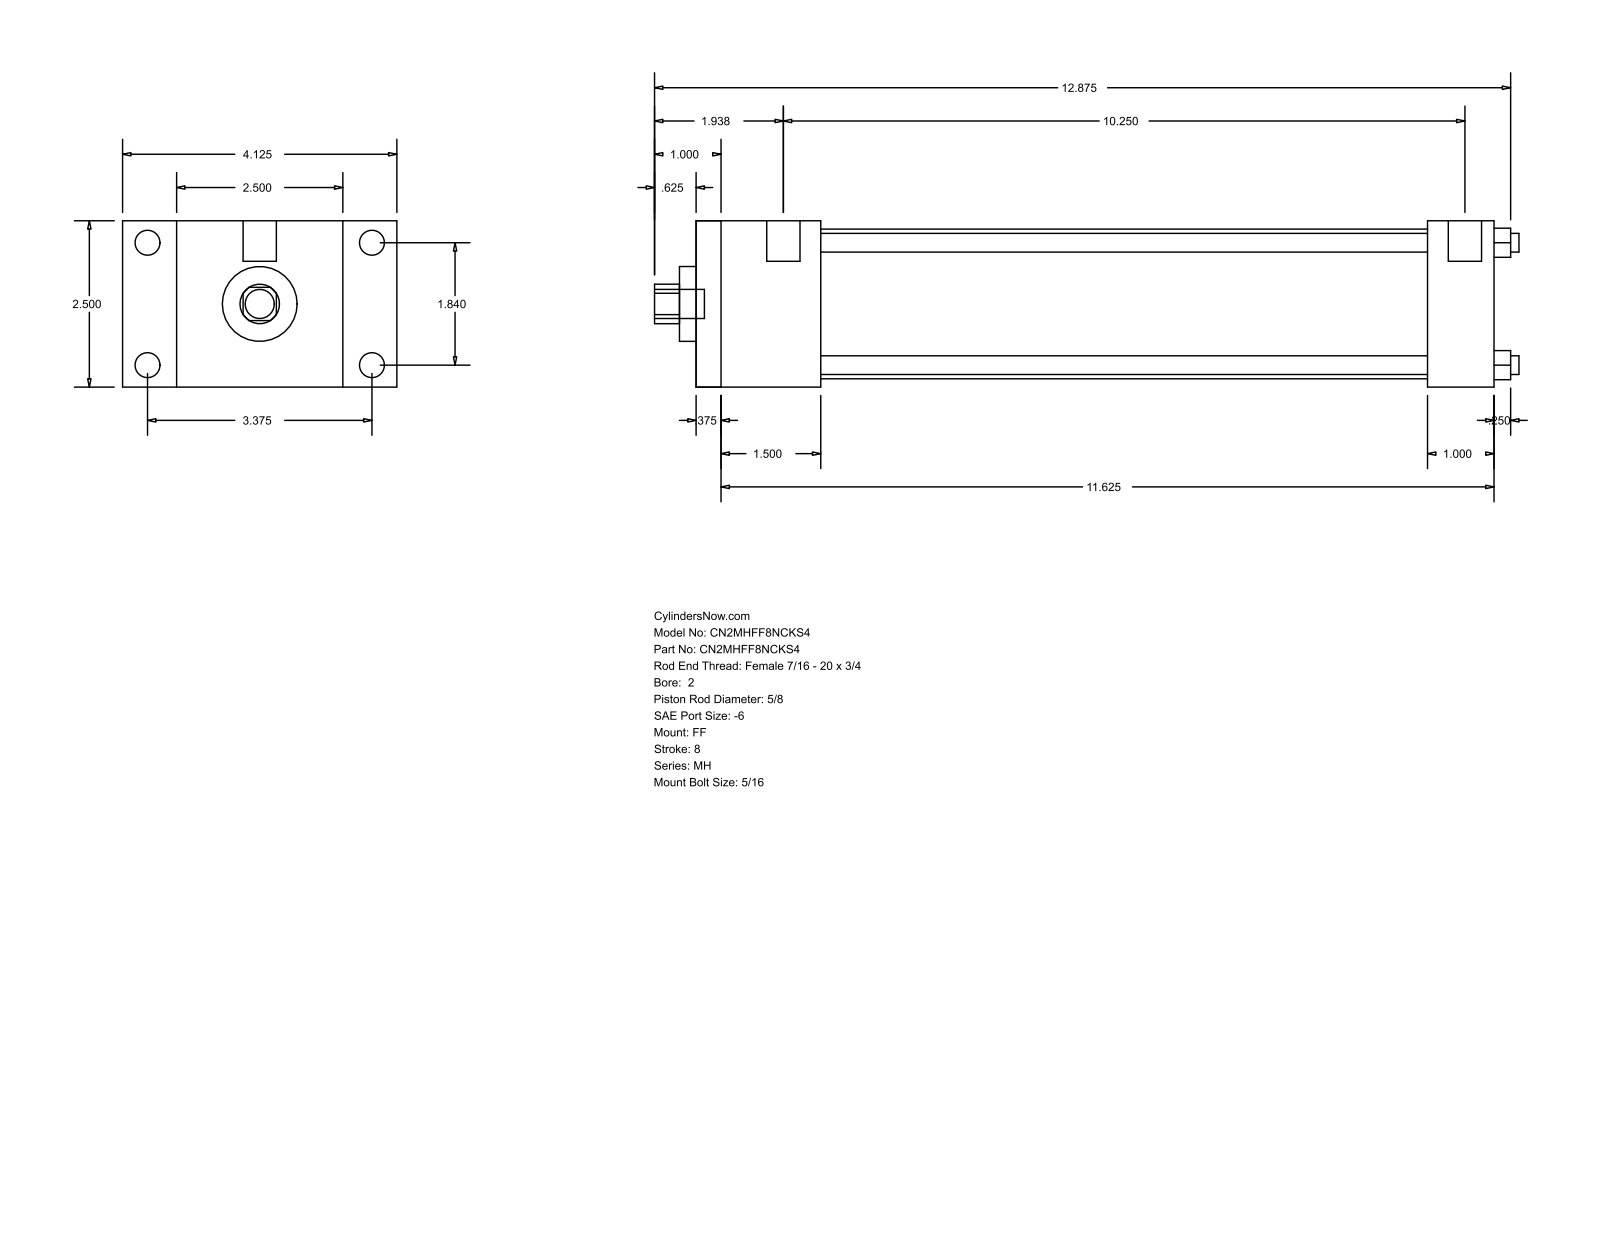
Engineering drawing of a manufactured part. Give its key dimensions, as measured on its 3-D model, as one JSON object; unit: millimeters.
{"part_name": "MH_FF__0200_0.625", "step_written_by": "GSSL Pune (CONFIG_CONTROL_DESIGN)", "units": "millimeters", "bodies": {"solids": 0, "faces": 92, "planar": 64, "cylindrical": 28, "other": 0}, "overall_size": [330.2, 104.78, 63.5], "round_holes": [[7.14, 4], [15.88, 1], [28.57, 1], [57.15, 1]], "round_bosses_or_shafts": [[9.53, 4], [5.56, 4], [12.7, 2], [11.11, 1]], "partial_cylinders_radius": [[7.54, 1]], "face_to_face_distances": [63.5, 304.8, 9.52, 295.28, 38.1, 47.62, 279.39, 269.87, 231.77, 257.18], "hole_center_spacings": [33.05, 46.74, 66.1]}
